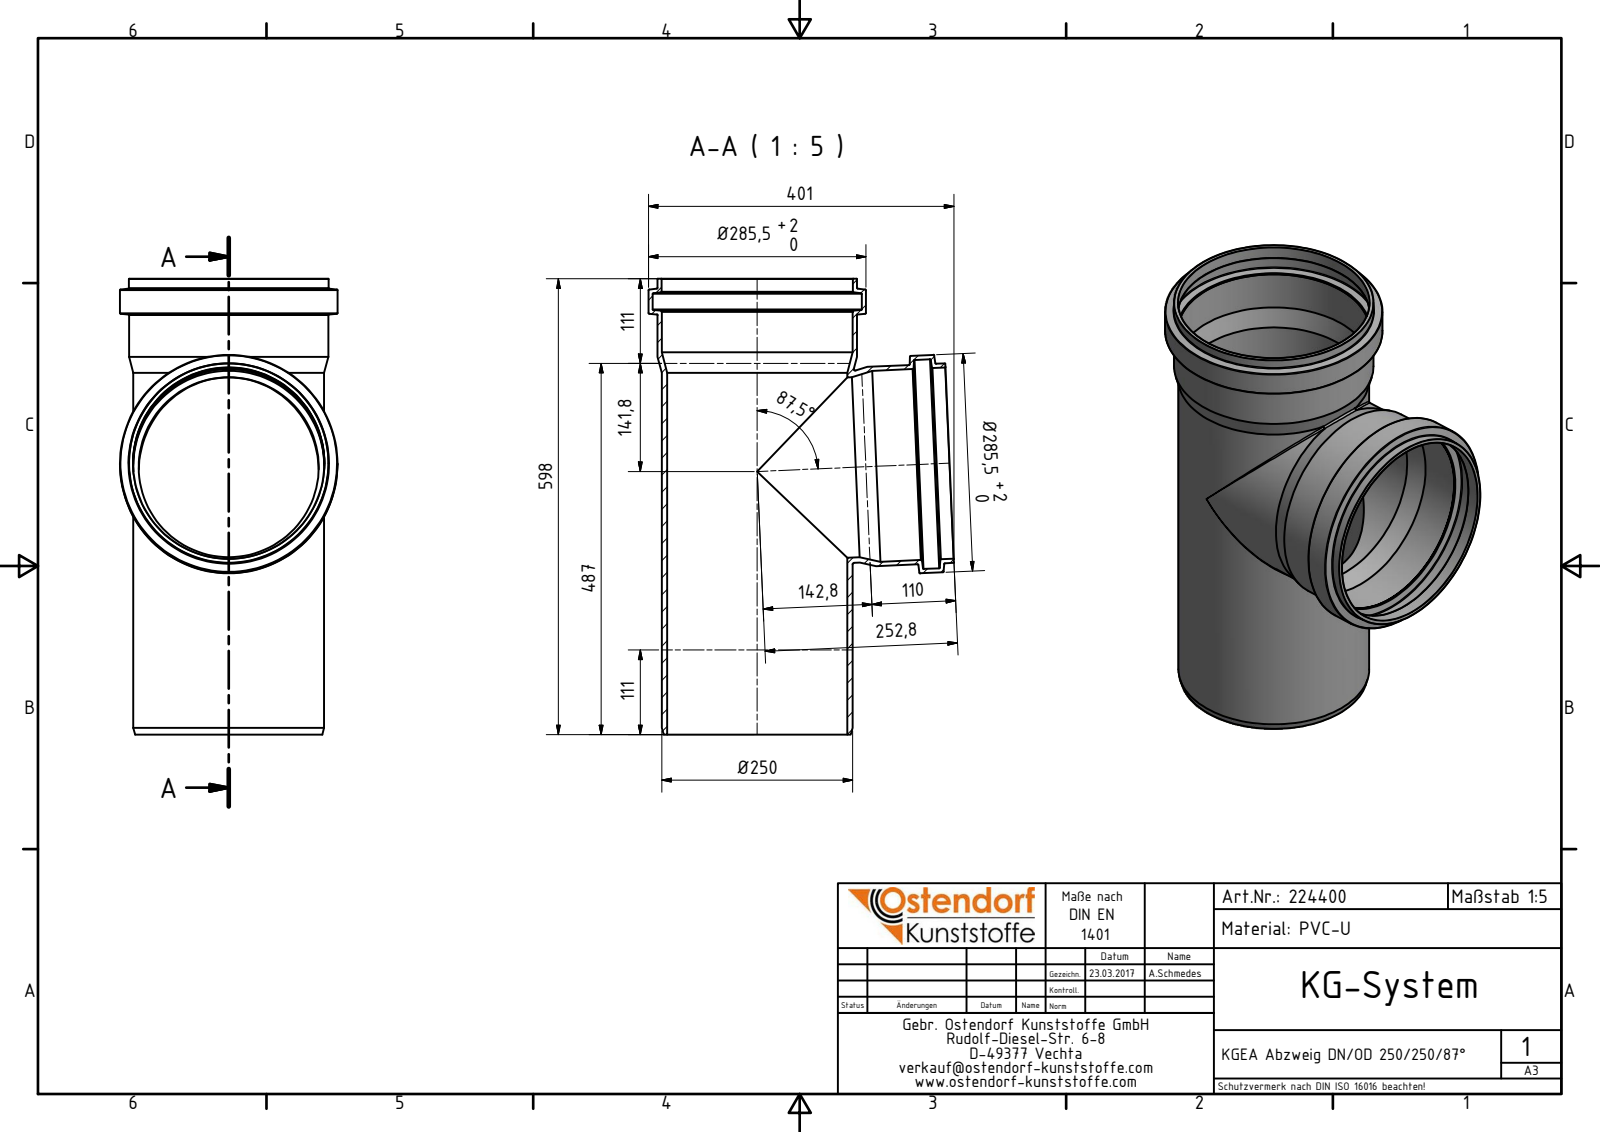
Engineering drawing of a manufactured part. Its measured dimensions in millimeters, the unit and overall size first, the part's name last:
Units: millimetres
Overall size (bounding box): 598 × 401 × 285.5
Round holes (diameter × count): ⌀251.1 ×3, ⌀236.3 ×2, ⌀250.8 ×2, ⌀274.5 ×2
Round bosses / shafts (diameter × count): ⌀285.5 ×2, ⌀262.1 ×2, ⌀261.8 ×2, ⌀250.5 ×2
Main face-to-face distances: 598, 554.77, 43.23, 43.22
Volume: 3 796 000 mm³ · Surface area: 1 171 000 mm²
Bodies: 1 solid, 60 faces (5 planar, 18 cylindrical, 37 other)
Part name (STEP PRODUCT): 224400 KGEA Abzweig DN_OD 250_250_87°
STEP written by: Autodesk Inventor 2016 (AUTOMOTIVE_DESIGN)
